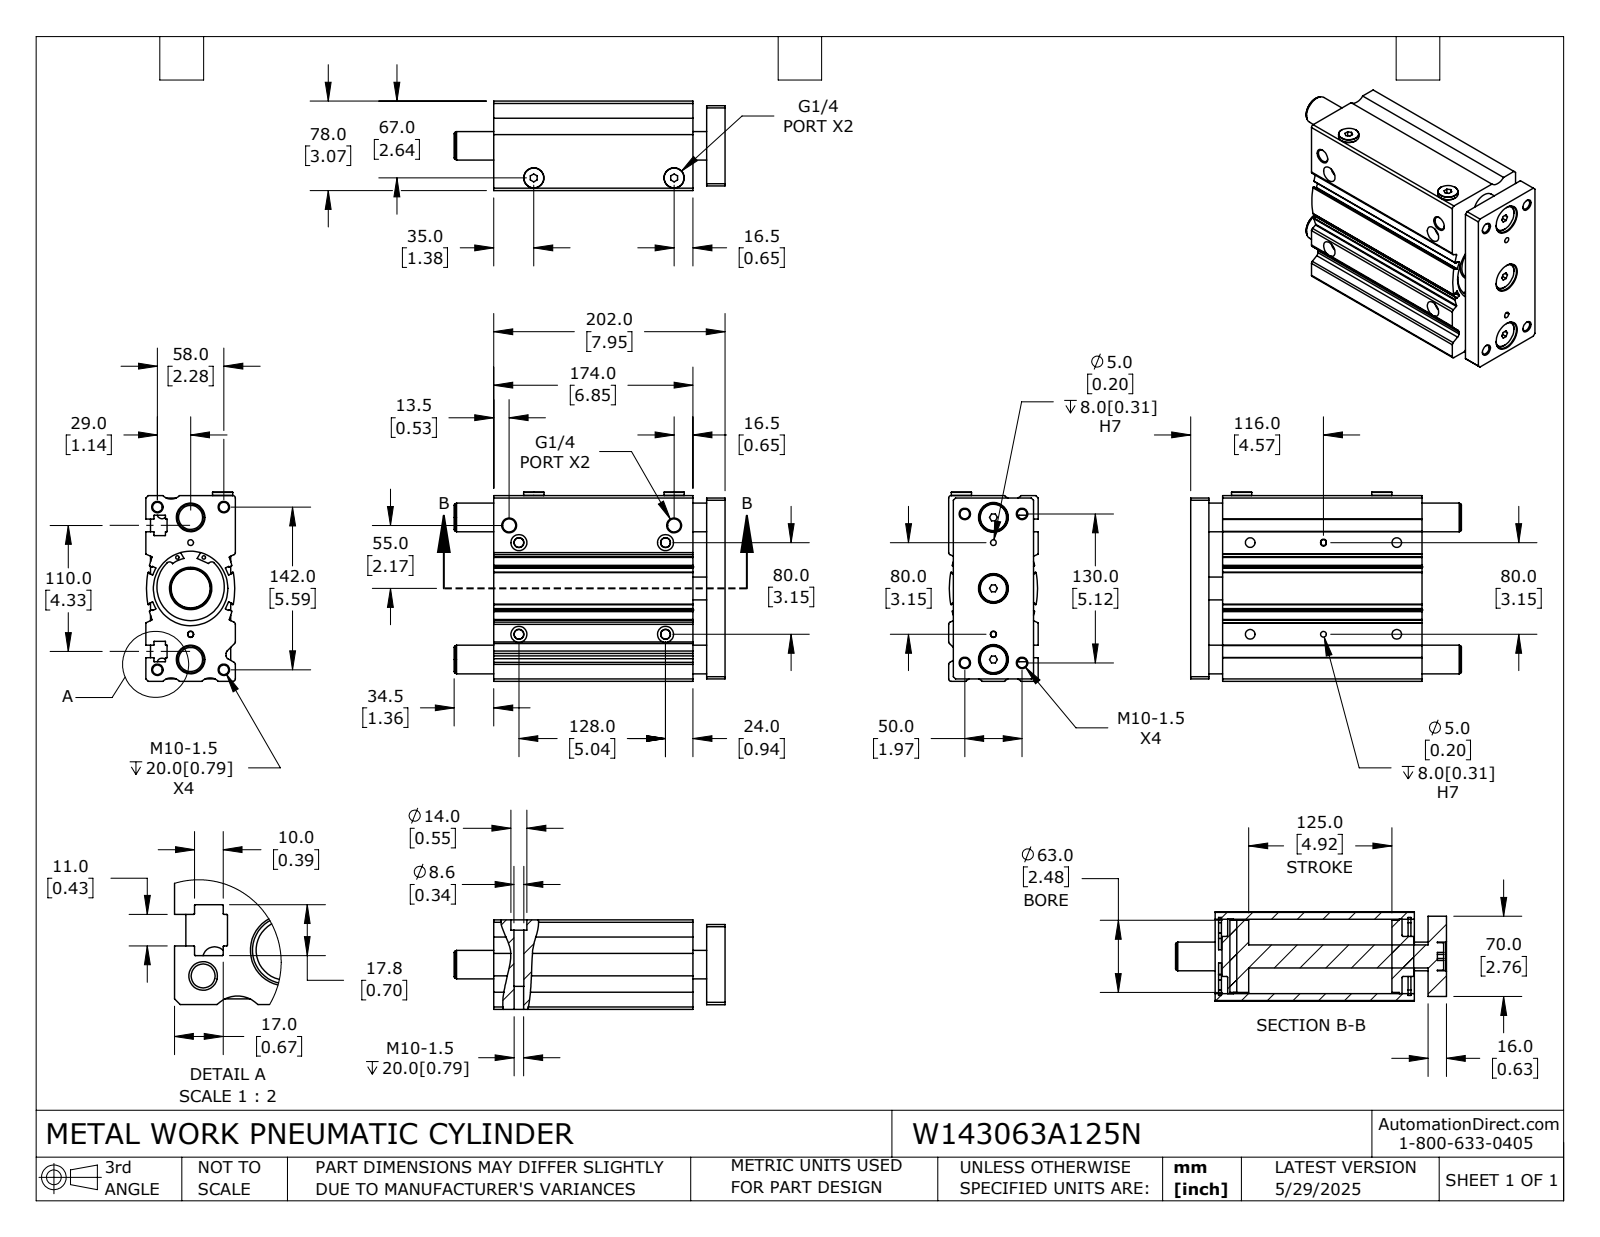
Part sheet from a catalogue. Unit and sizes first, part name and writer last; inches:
Units: inches
Overall size (bounding box): 9.311 × 6.496 × 3.071
Round holes (diameter × count): ⌀0.33 ×12, ⌀0.118 ×4, ⌀0.197 ×4, ⌀0.339 ×4, ⌀0.551 ×4, ⌀0.984 ×3, ⌀0.448 ×2, ⌀2.559 ×1
Round bosses / shafts (diameter × count): ⌀0.945 ×3, ⌀0.697 ×2, ⌀2.677 ×1, ⌀2.551 ×1, ⌀2.48 ×1, ⌀1.378 ×1, ⌀0.787 ×1
Partial cylindrical surfaces — rounded edges, fillets, slot ends (radius × count): R0.012 ×44, R0.02 ×12, R0.079 ×8, R0.098 ×4, R0.118 ×4, R0.394 ×3, R0.124 ×2, R1.157 ×2
Main face-to-face distances: 3.071, 0.63, 6.378, 0.472, 1.102, 7.953, 7.323, 6.85, 4.331, 5.571
Hole centre spacings: 0.284, 0.682, 0.991, 1.158, 1.195, 1.392, 1.448, 1.585
Volume: 108.9 in³ · Surface area: 487.5 in²
Bodies: 6 solids, 454 faces (182 planar, 216 cylindrical, 56 other)
Part name (STEP PRODUCT): W143063A125N_ROD; W143063A125N_BODY; W143063A125N
STEP written by: SolidWorks 2024 (CONFIG_CONTROL_DESIGN)
